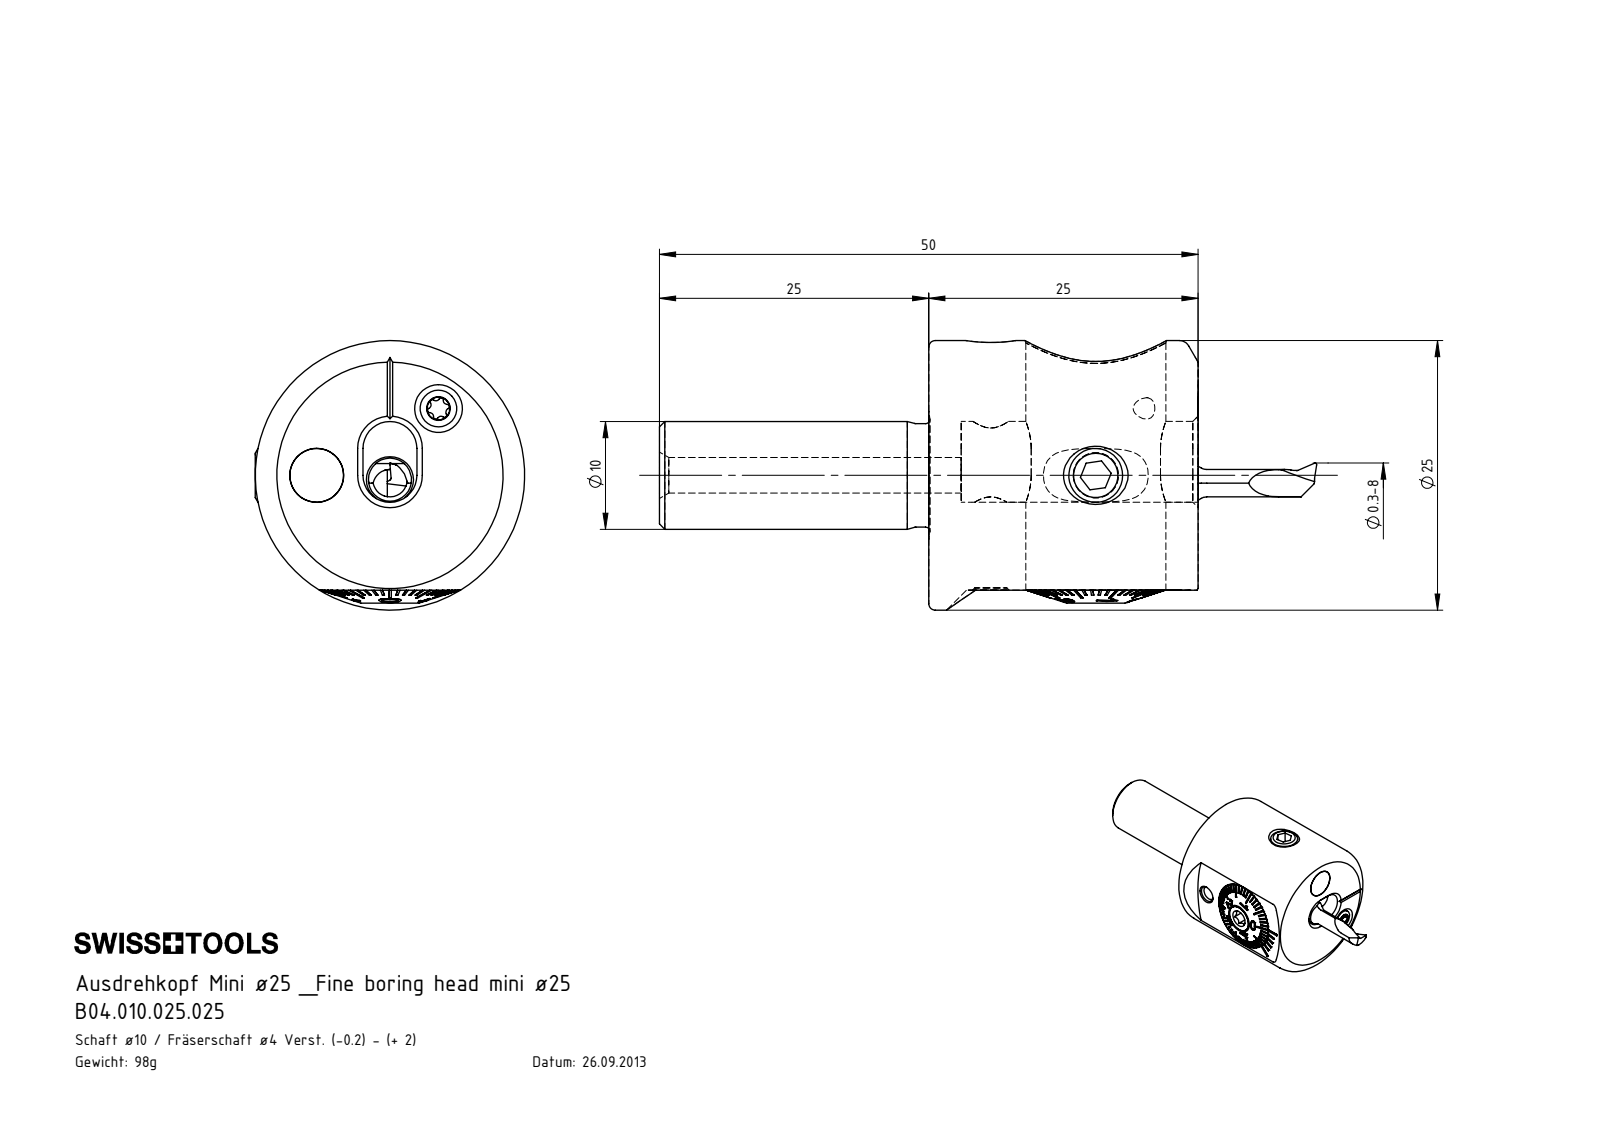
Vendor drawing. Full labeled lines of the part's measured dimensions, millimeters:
Part name (STEP PRODUCT): DIN 3771 - 11x1; F25-BG2.013.003_A; ISO 4026 - M4 x 8; B04.010.025.025 (+8 more)
STEP written by: SolidWorks 2017 (CONFIG_CONTROL_DESIGN)
Units: millimetres
Bodies: 16 solids, 741 faces (313 planar, 138 cylindrical, 290 other)
Overall size (bounding box): 61 × 25 × 25
Volume: 12 767 mm³ · Surface area: 9 402 mm²
Round holes (diameter × count): ⌀3.3 ×4, ⌀2 ×2, ⌀4.2 ×2, ⌀5 ×2, ⌀1 ×1, ⌀2.4 ×1, ⌀2.7 ×1, ⌀3 ×1, ⌀4 ×1, ⌀6.75 ×1, ⌀7.3 ×1, ⌀7.4 ×1
Round bosses / shafts (diameter × count): ⌀4 ×3, ⌀4.95 ×2, ⌀25 ×1, ⌀13 ×1, ⌀12.98 ×1, ⌀12.85 ×1, ⌀10.65 ×1, ⌀10 ×1
Partial cylindrical surfaces — rounded edges, fillets, slot ends (radius × count): R0.21 ×6, R0.36 ×5, R0.2 ×4, R2.2 ×4, R1.6 ×2, R2.5 ×2, R0.36 ×1, R0.5 ×1
Main face-to-face distances: 25, 3.9, 1.5, 0.8, 3.1, 3.8, 1.6, 2.3, 8, 3
Hole centre spacings: 3.5, 7.66, 0.4, 6.25, 6.8, 6.81, 7, 7.99
